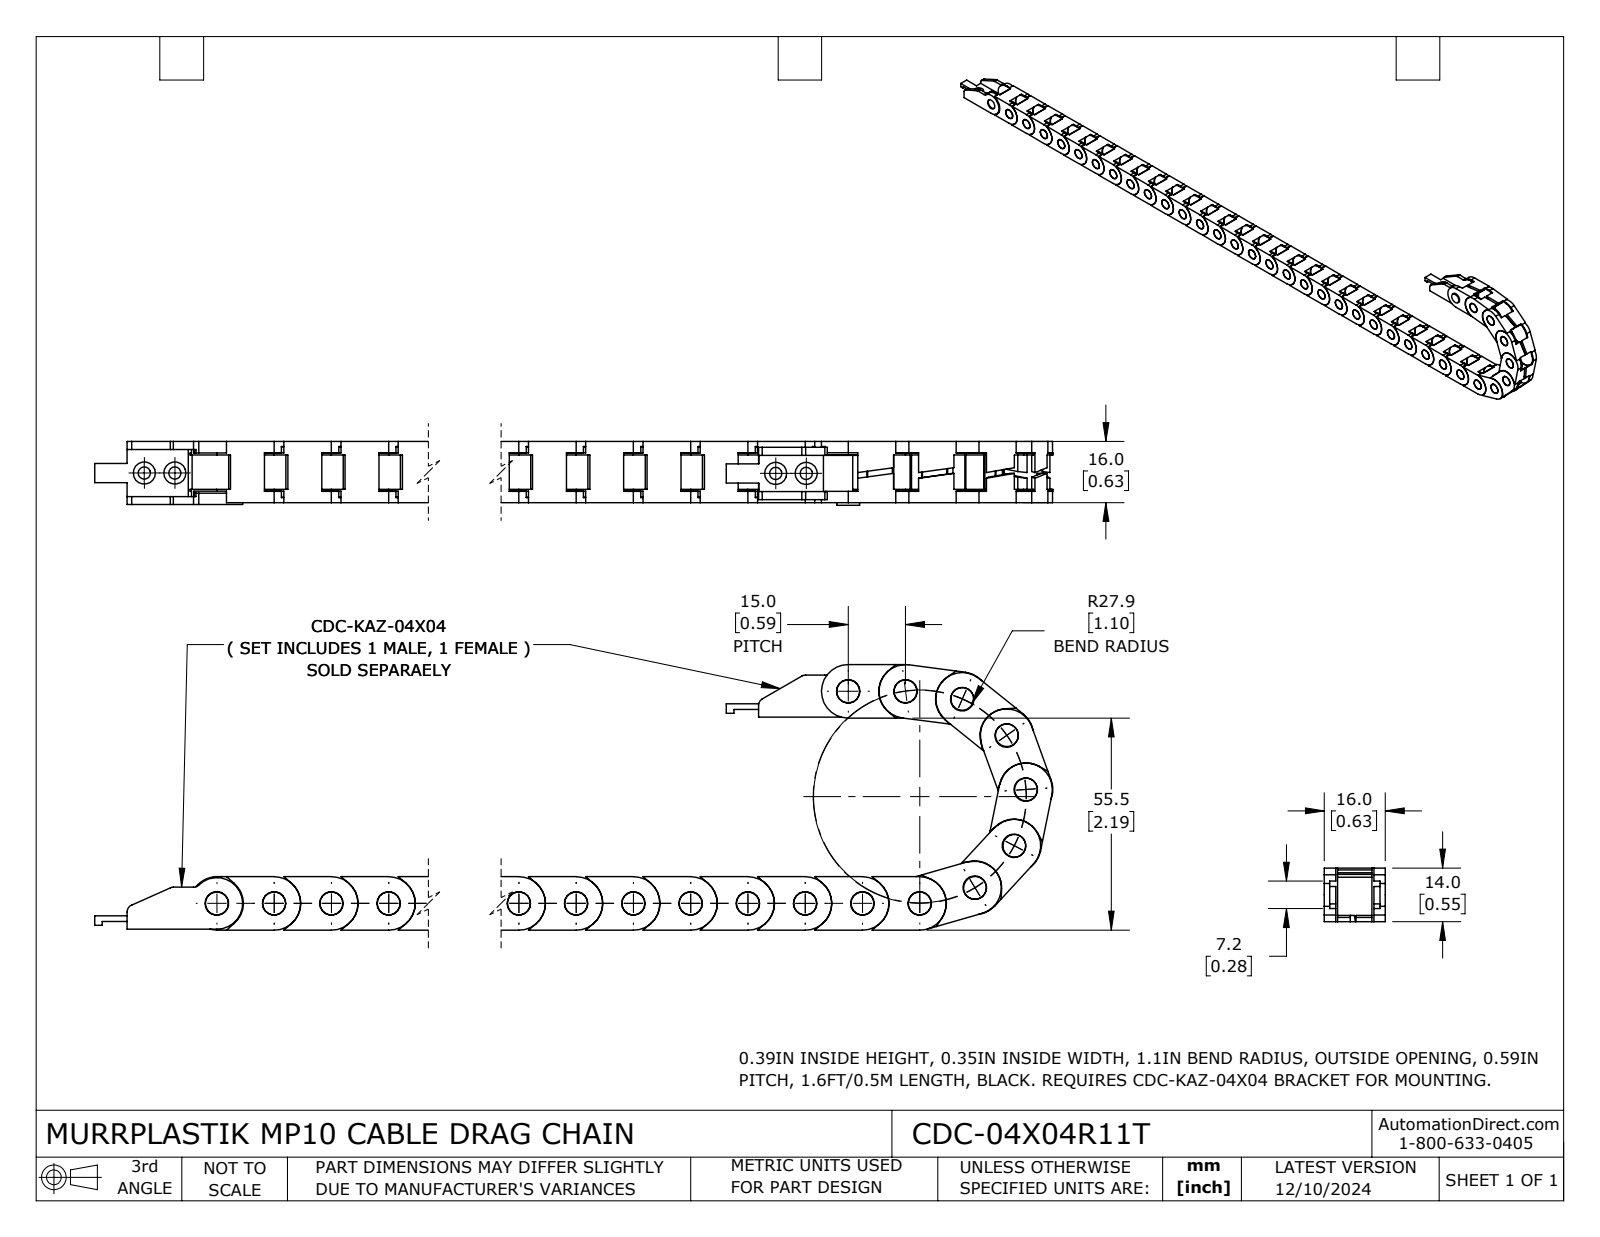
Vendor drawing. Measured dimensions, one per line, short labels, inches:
name: CDC-04X04R11T
written by: SolidWorks 2024 (AUTOMOTIVE_DESIGN)
unit: in
bodies: 36 solids, 2442 faces (1654 planar, 784 cylindrical, 4 other)
size: 19.168 × 2.737 × 0.657
volume: 3.562 in³; area: 128.5 in²
holes: 34× ⌀0.242, 4× ⌀0.126, 1× ⌀0.244
bosses: 35× ⌀0.236, 28× ⌀0.551
rounds: 170× R0.02, 40× R0.274, 34× R0.142, 34× R0.457, 12× R0.276, 6× R0.079, 2× R0.039, 2× R0.266
face distances: 0.138, 0.492, 0.354, 0.63, 0.087, 0.02, 0.051, 0.063, 0.461, 0.512
hole spacings: 0.591, 1.181, 1.772, 2.362, 2.953, 3.543, 4.134, 4.724
